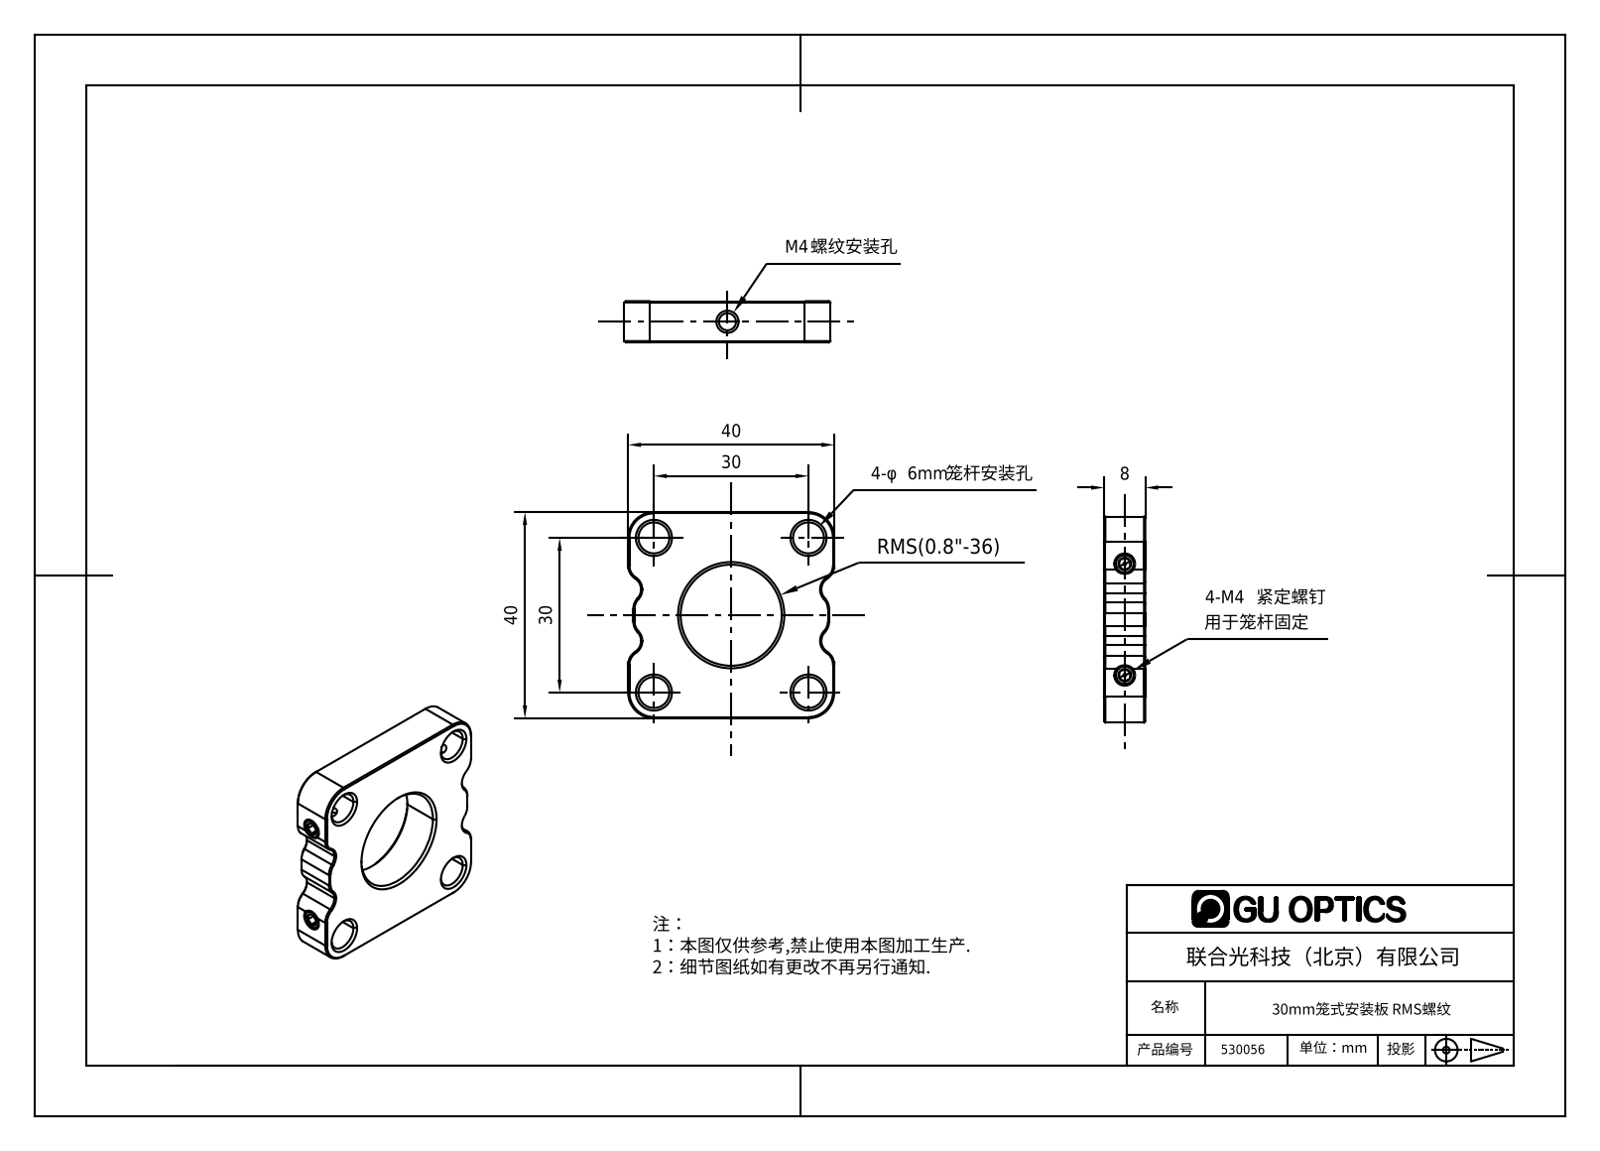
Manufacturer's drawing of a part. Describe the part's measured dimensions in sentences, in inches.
The part is named "2.2.1.16_L30B-RMS_30 mm笼板，带RMS螺纹，M4螺纹". Its 3-D file was written by "SolidWorks 2018 (AUTOMOTIVE_DESIGN)". It is 0 solids with 210 faces: 58 planar, 38 cylindrical and 114 other. Overall it measures 1.575 by 1.575 by 0.315 inches. Round holes: 4 of diameter 0.236, 3 of diameter 0.13, 1 of diameter 0.772. Partial cylindrical surfaces (rounded edges, fillets, slot ends): 8 of radius 0.118, 4 of radius 0.098, 4 of radius 0.197. The main face-to-face distances are 0.315, 1.575, 0.039, 1.535, 1.322, 0.083, 1.496, 0.675, 0.786, 0.028. The hole center spacings are 0.835, 1.181, 1.67, 0.85.
